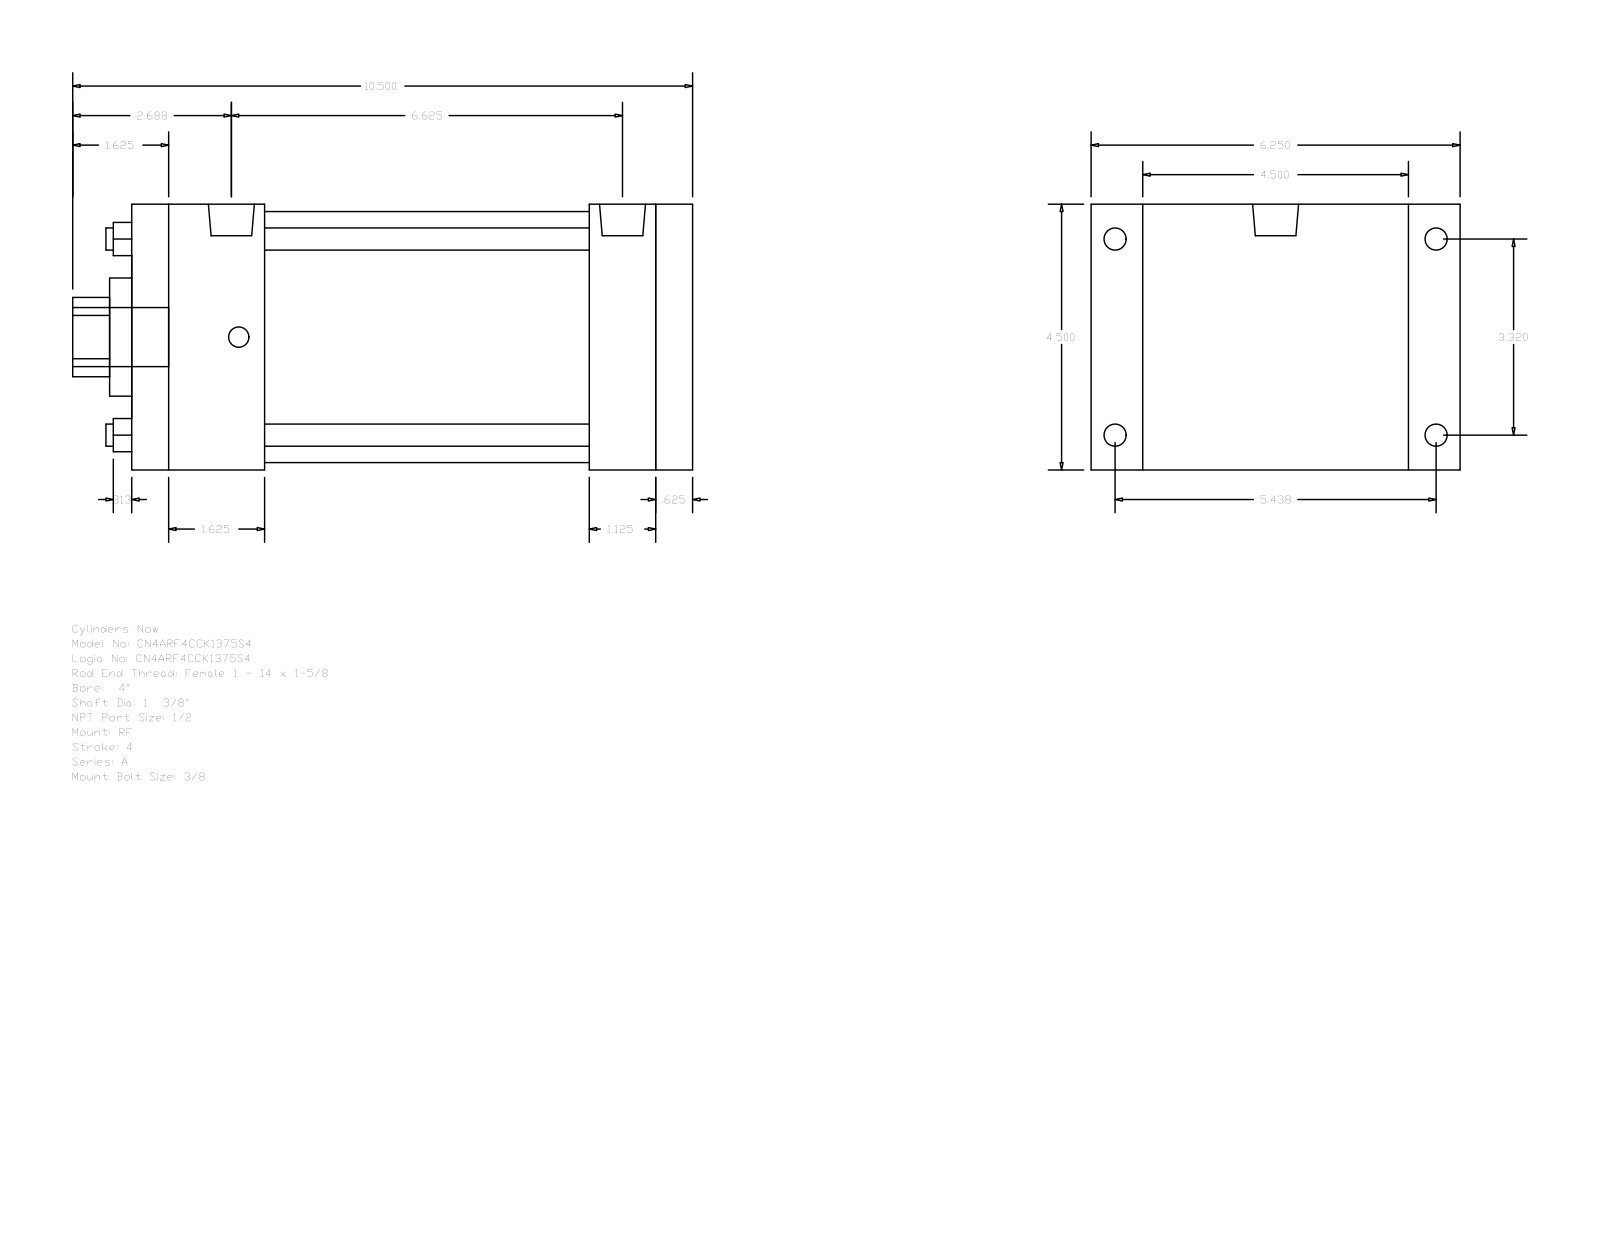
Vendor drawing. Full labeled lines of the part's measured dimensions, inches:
Part name (STEP PRODUCT): A_RF__0400_1.375
STEP written by: GSSL Pune (CONFIG_CONTROL_DESIGN)
Units: inches
Bodies: 0 solids, 92 faces (64 planar, 28 cylindrical, 0 other)
Overall size (bounding box): 10.5 × 6.25 × 4.5
Round holes (diameter × count): ⌀0.375 ×4, ⌀1.375 ×1, ⌀2 ×1, ⌀4.25 ×1
Round bosses / shafts (diameter × count): ⌀0.375 ×4, ⌀0.344 ×4, ⌀0.778 ×2, ⌀1 ×1
Partial cylindrical surfaces — rounded edges, fillets, slot ends (radius × count): R0.672 ×1
Main face-to-face distances: 4.5, 9.5, 0.625, 8.875, 1.125, 0.875, 5.375, 7.75, 1.75, 2.25
Hole centre spacings: 2.347, 3.32, 4.695
